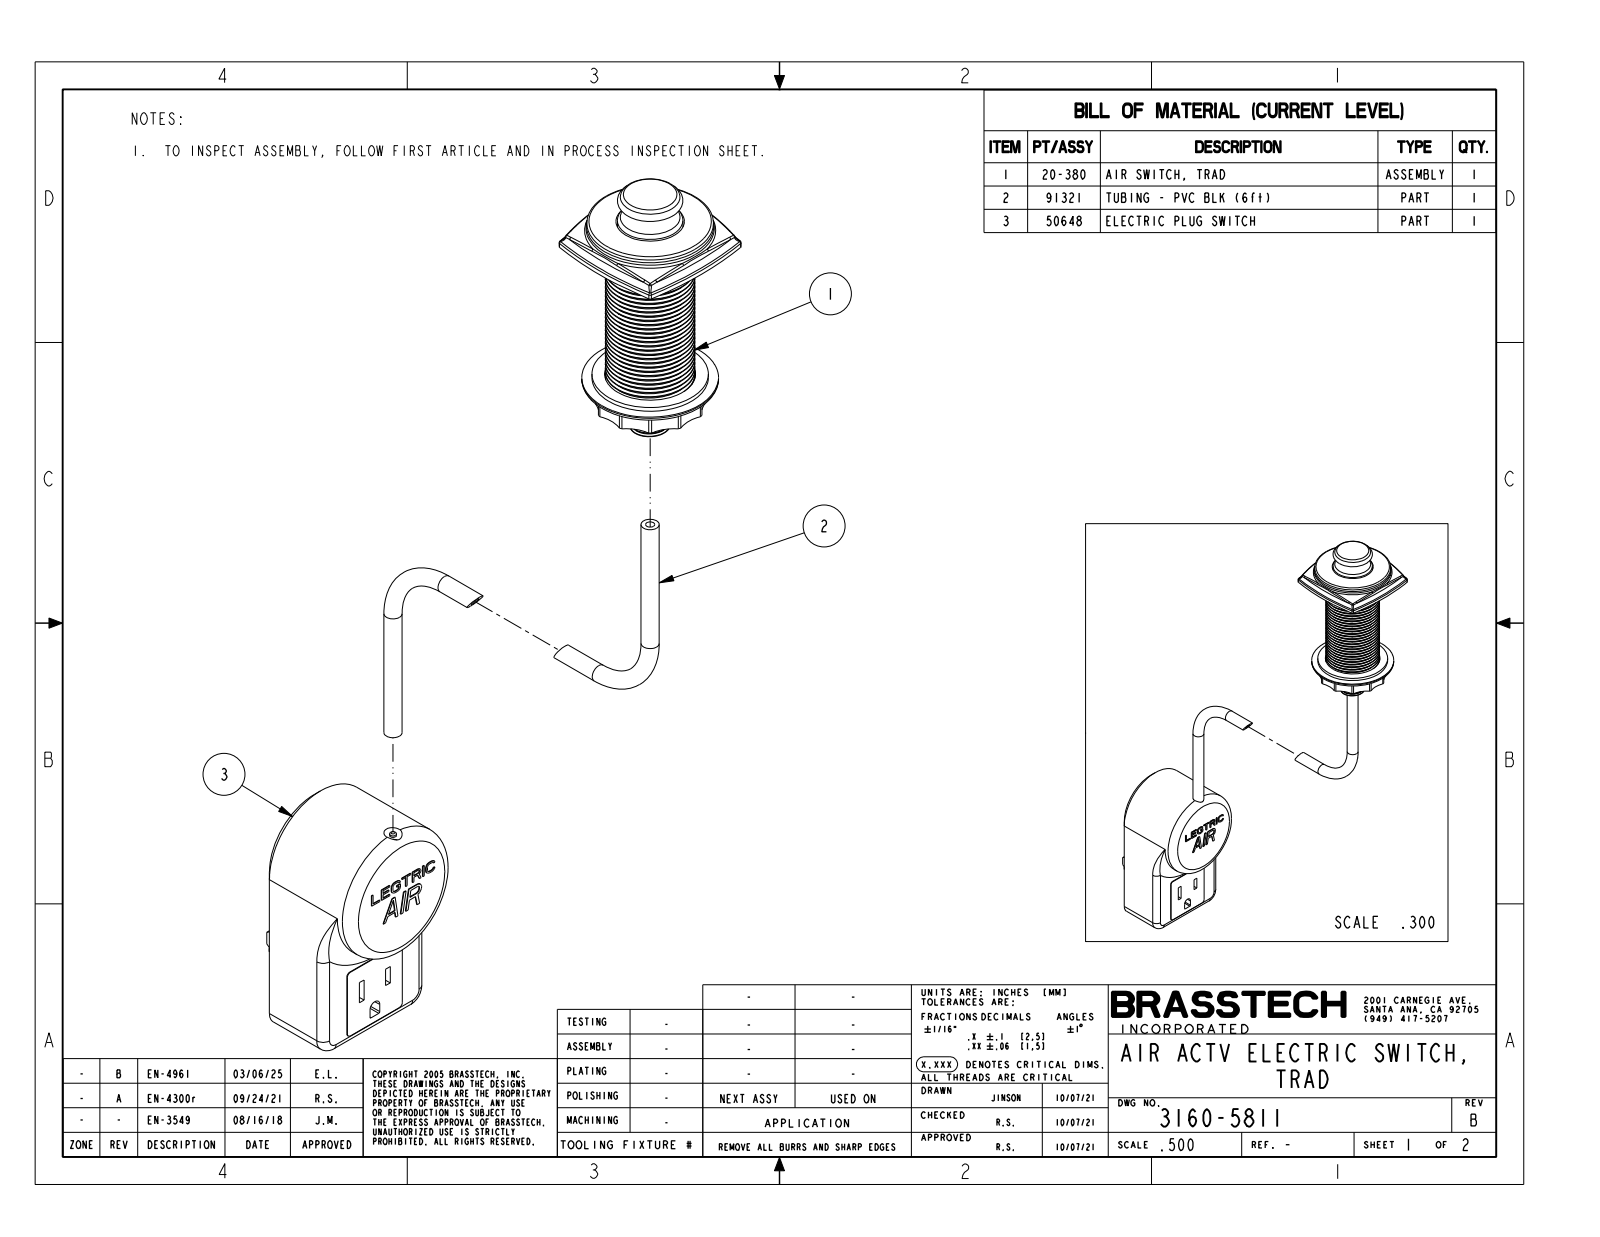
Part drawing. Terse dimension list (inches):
name: 3160-5811
written by: CREO PARAMETRIC BY PTC INC, 2018400 (AUTOMOTIVE_DESIGN)
unit: in
bodies: 3 solids, 534 faces (253 planar, 159 cylindrical, 122 other)
size: 12.984 × 8.338 × 1.99
volume: 14.34 in³; area: 70.7 in²
holes: 4× ⌀0.125, 1× ⌀0.94, 1× ⌀1.25
bosses: 3× ⌀0.25, 1× ⌀1.99, 1× ⌀1.88, 1× ⌀1.6, 1× ⌀1.23, 1× ⌀1.153, 1× ⌀1.135, 1× ⌀0.9
rounds: 12× R0.5, 4× R0.03, 4× R0.06, 4× R5.18, 4× R5.25, 3× R0.125, 2× R0.02, 2× R0.25
face distances: 1.99, 1.7, 0.08, 0.425, 0.36, 12.059, 12.484, 0.52, 1.18, 0.44
hole spacings: 5
